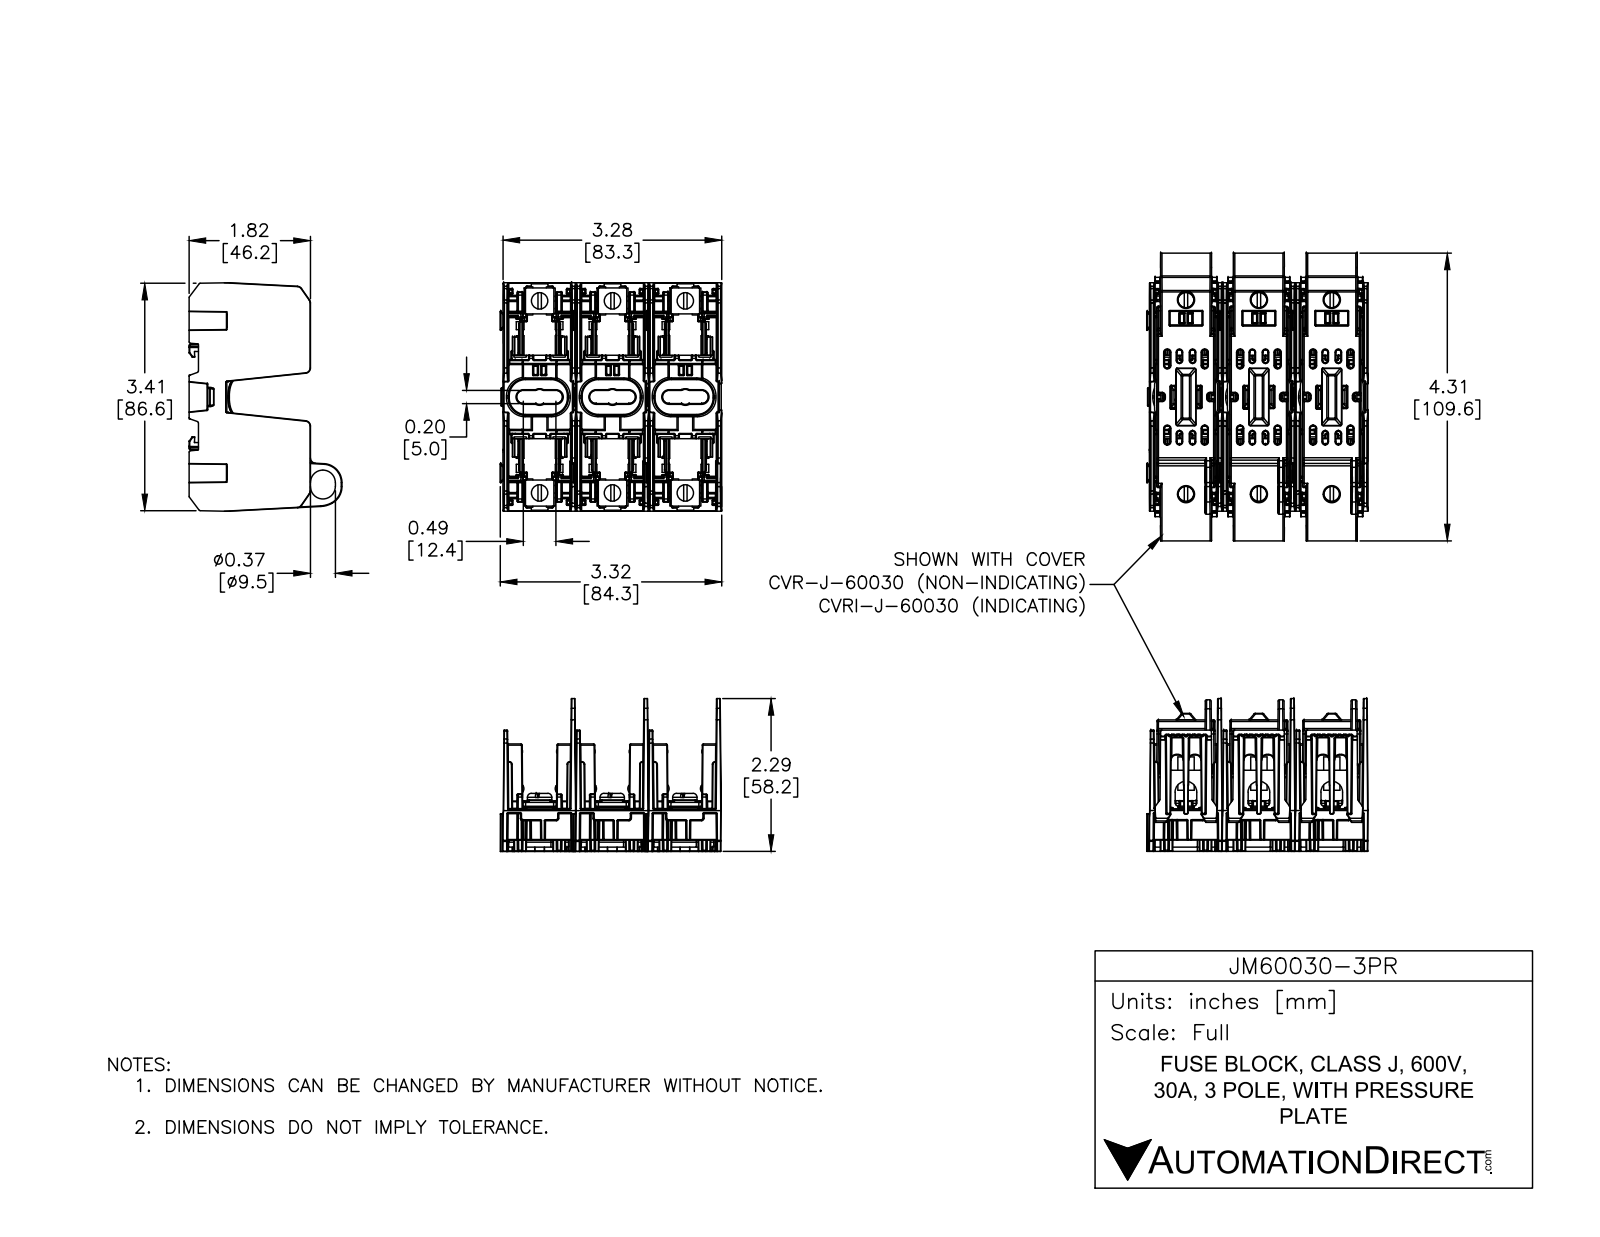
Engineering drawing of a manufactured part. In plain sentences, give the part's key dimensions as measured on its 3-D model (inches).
The part is named "JM60030-3PR; JM60030-1CR". Its 3-D file was written by "SolidWorks 2016 (AUTOMOTIVE_DESIGN)". It is 39 solids with 9279 faces: 2343 planar, 3987 cylindrical and 2949 other. Overall it measures 3.433 by 3.312 by 2.291 inches. Its volume is 5.927 cubic inches and its surface area 154.9 square inches. Round holes: 6 of diameter 0.225, 6 of diameter 0.244. Round bosses or shafts: 6 of diameter 0.244. Partial cylindrical surfaces (rounded edges, fillets, slot ends): 1104 of radius 0.01, 855 of radius 0.006, 119 of radius 0.02, 88 of radius 0.039, 72 of radius 0.004, 24 of radius 0.02, 18 of radius 0.059, 13 of radius 0.079. The main face-to-face distances are 1.089, 1.089, 2.178, 1.013, 0.075, 0.024, 1.014, 2.102, 1.164, 1.164. The hole center spacings are 2.531, 1.089, 1.089, 1.241, 1.241, 2.01, 2.178, 2.257.
